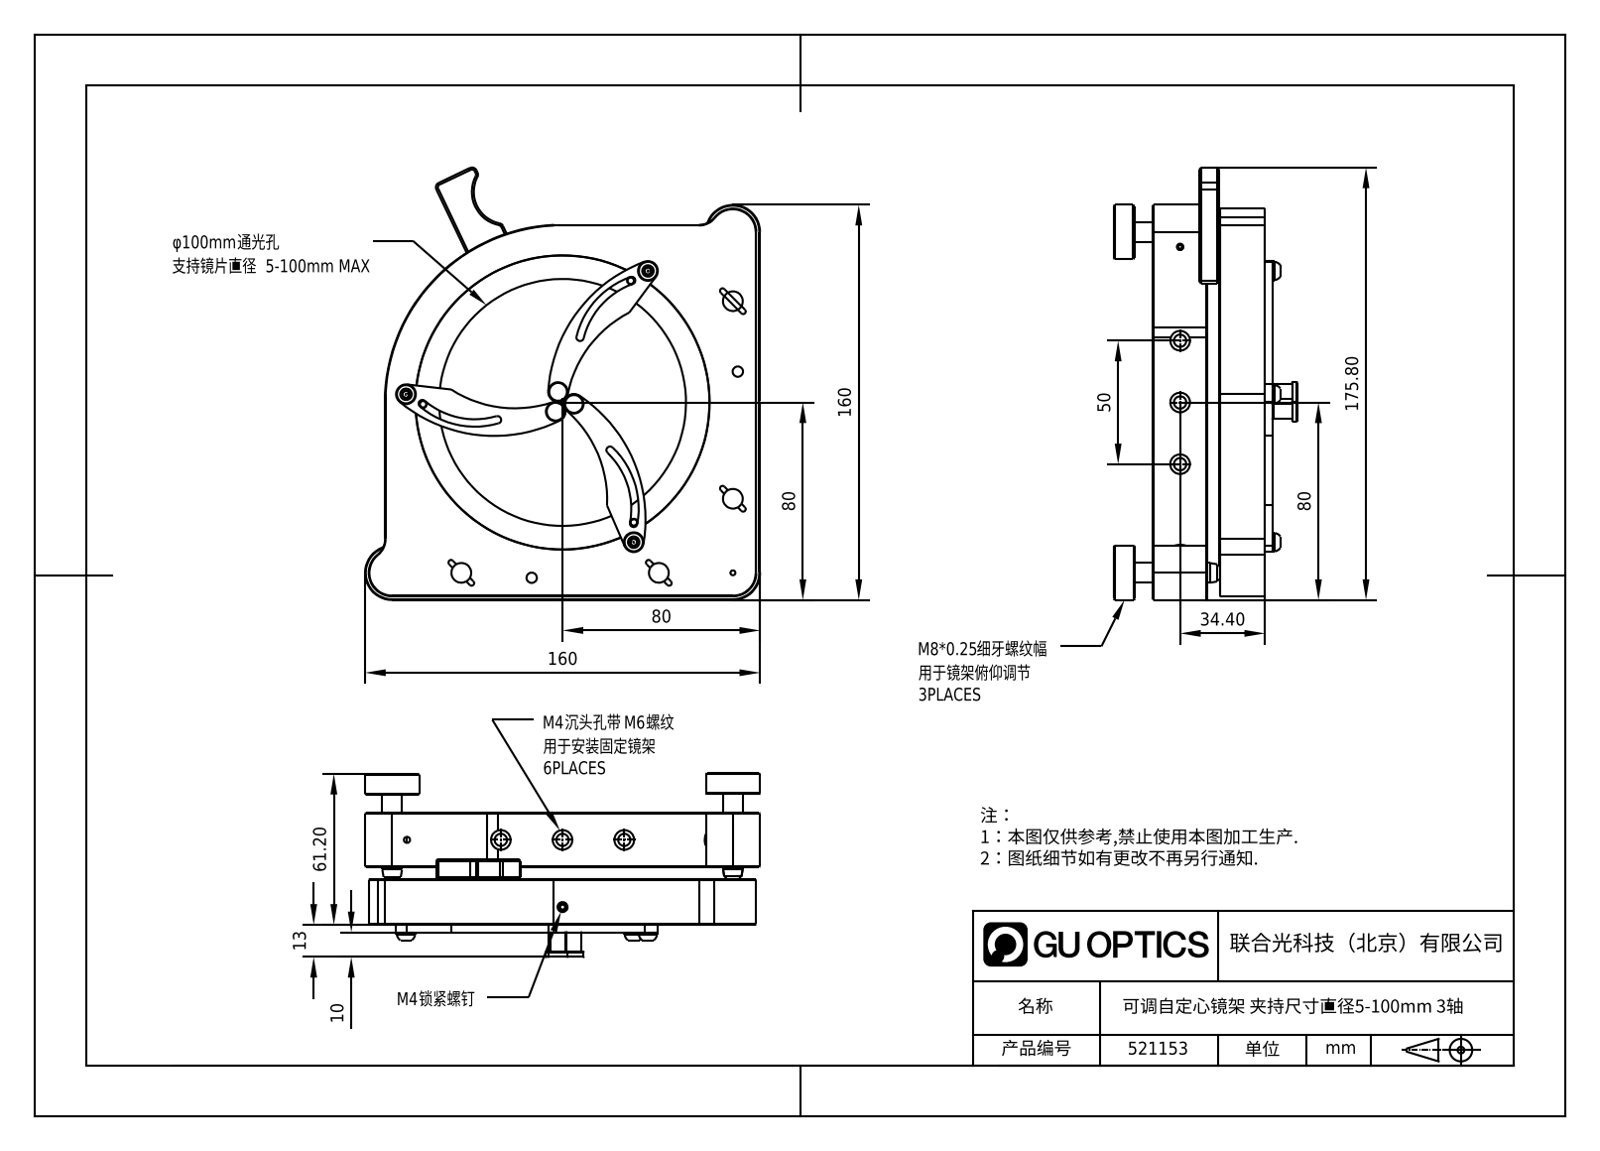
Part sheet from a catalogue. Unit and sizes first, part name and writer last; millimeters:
Units: millimetres
Overall size (bounding box): 175.16 × 160 × 74.64
Round holes (diameter × count): ⌀2.5 ×16, ⌀5 ×14, ⌀8 ×13, ⌀2.05 ×8, ⌀2.9 ×8, ⌀6 ×8, ⌀3.3 ×7, ⌀4.2 ×5, ⌀3 ×3, ⌀7.75 ×3, ⌀8.5 ×3, ⌀9 ×3
Round bosses / shafts (diameter × count): ⌀4.6 ×8, ⌀2.5 ×8, ⌀4 ×7, ⌀3 ×4, ⌀22 ×3, ⌀13 ×3, ⌀12 ×3, ⌀11 ×3
Partial cylindrical surfaces — rounded edges, fillets, slot ends (radius × count): R1.05 ×12, R1.5 ×6, R2 ×6, R6 ×4, R1 ×3, R4 ×3, R9.5 ×3, R31.5 ×3
Main face-to-face distances: 18.6, 22, 3.6, 15, 3.4, 18.4, 5, 4.8, 8.4, 23.4
Hole centre spacings: 61, 97.93, 74.96, 40.56, 53, 5.32, 25, 110.48
Volume: 367 819 mm³ · Surface area: 135 764 mm²
Bodies: 56 solids, 1432 faces (446 planar, 522 cylindrical, 464 other)
Part name (STEP PRODUCT): 1.1.4.5_ZJX-100-3
STEP written by: SolidWorks 2021 (CONFIG_CONTROL_DESIGN)
